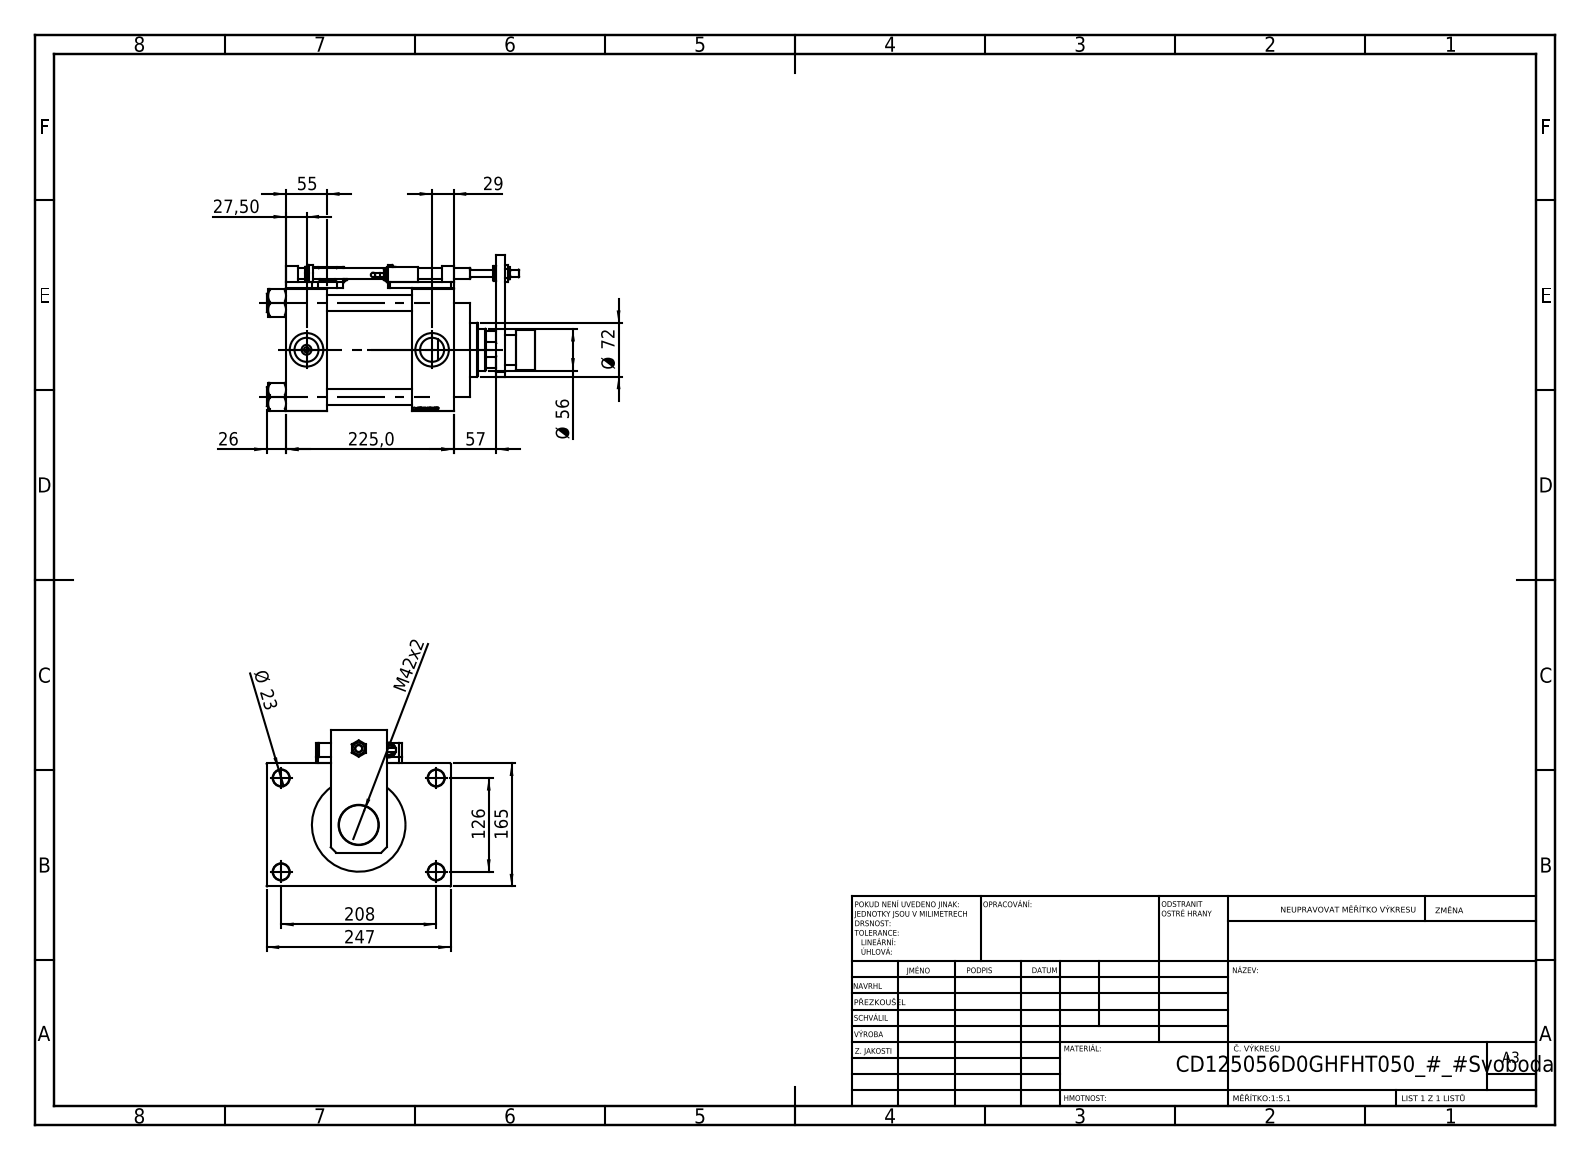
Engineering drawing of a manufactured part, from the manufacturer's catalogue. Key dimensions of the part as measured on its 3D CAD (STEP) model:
Part name (STEP PRODUCT): V215CD_SWITCH_Q_TYC; V215CD_SWITCH_Q_MAGNET; V215CD_SWITCH_Q_DIMA; V215CD_SWITCH_Q_PODLOZKA_BACK (+7 more)
STEP written by: SolidWorks 2019 (CONFIG_CONTROL_DESIGN)
Units: millimetres
Bodies: 25 solids, 1390 faces (669 planar, 158 cylindrical, 563 other)
Overall size (bounding box): 360 × 247 × 210
Volume: 5 550 000 mm³ · Surface area: 691 850 mm²
Round holes (diameter × count): ⌀22 ×8, ⌀8.5 ×4, ⌀13.5 ×4, ⌀7 ×2, ⌀32.24 ×2, ⌀45 ×2, ⌀10 ×1, ⌀14 ×1, ⌀40.5 ×1, ⌀42 ×1, ⌀56 ×1, ⌀59 ×1
Round bosses / shafts (diameter × count): ⌀25 ×4, ⌀20 ×3, ⌀16 ×2, ⌀14 ×2, ⌀6 ×2, ⌀131 ×1, ⌀72 ×1, ⌀54 ×1
Partial cylindrical surfaces — rounded edges, fillets, slot ends (radius × count): R7.5 ×4
Main face-to-face distances: 165, 55, 169, 114, 225, 170, 56, 173, 8, 41
Hole centre spacings: 41.05, 89.02, 121.59, 125.9, 132.47, 166.95, 209.13, 32
